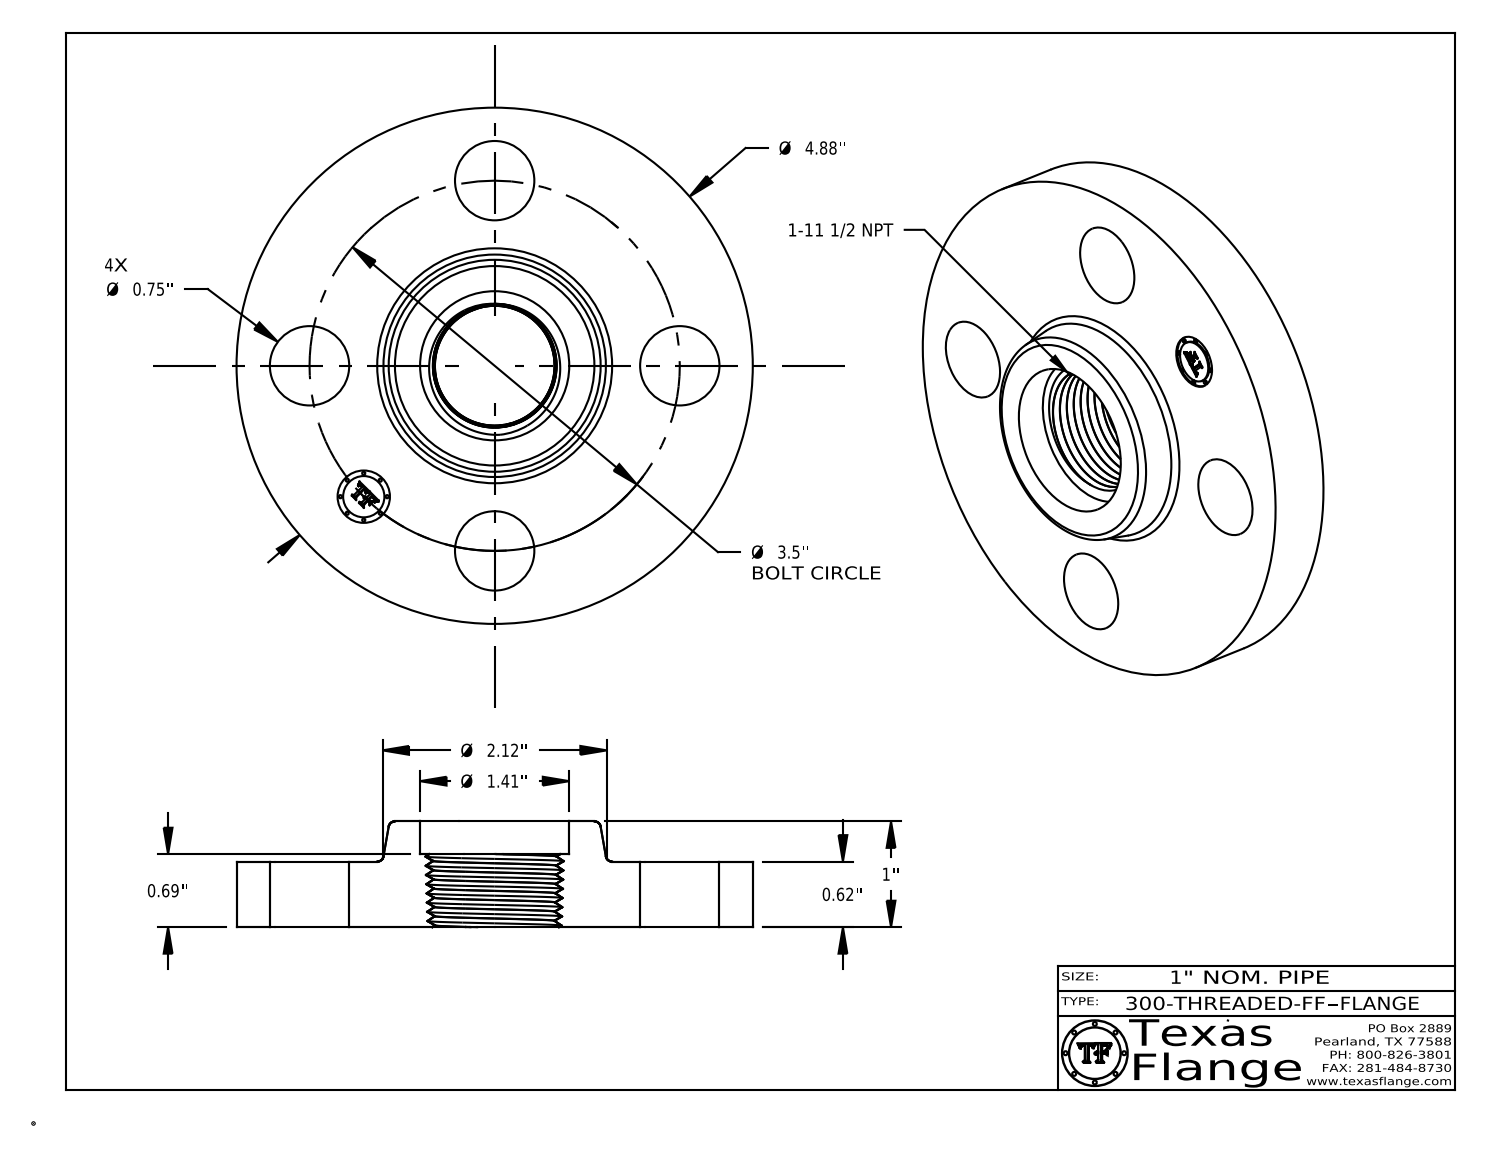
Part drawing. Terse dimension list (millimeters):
name: 300-THREADED-FF
written by: CATIA V5 STEP AP214 (AUTOMOTIVE_DESIGN)
unit: mm
bodies: 1 solid, 492 faces (369 planar, 32 cylindrical, 91 other)
size: 124 × 124 × 25.4
volume: 171 600 mm³; area: 35 570 mm²
holes: 4× ⌀19.1, 1× ⌀12.6, 1× ⌀35.8
bosses: 8× ⌀0.8, 1× ⌀124, 1× ⌀9.9
face distances: 15.7, 25.4, 9.7, 1.8, 17.5, 7.9, 2.2, 0.4, 15.4, 10
hole spacings: 44.5, 62.9, 34, 82.1, 88.9
